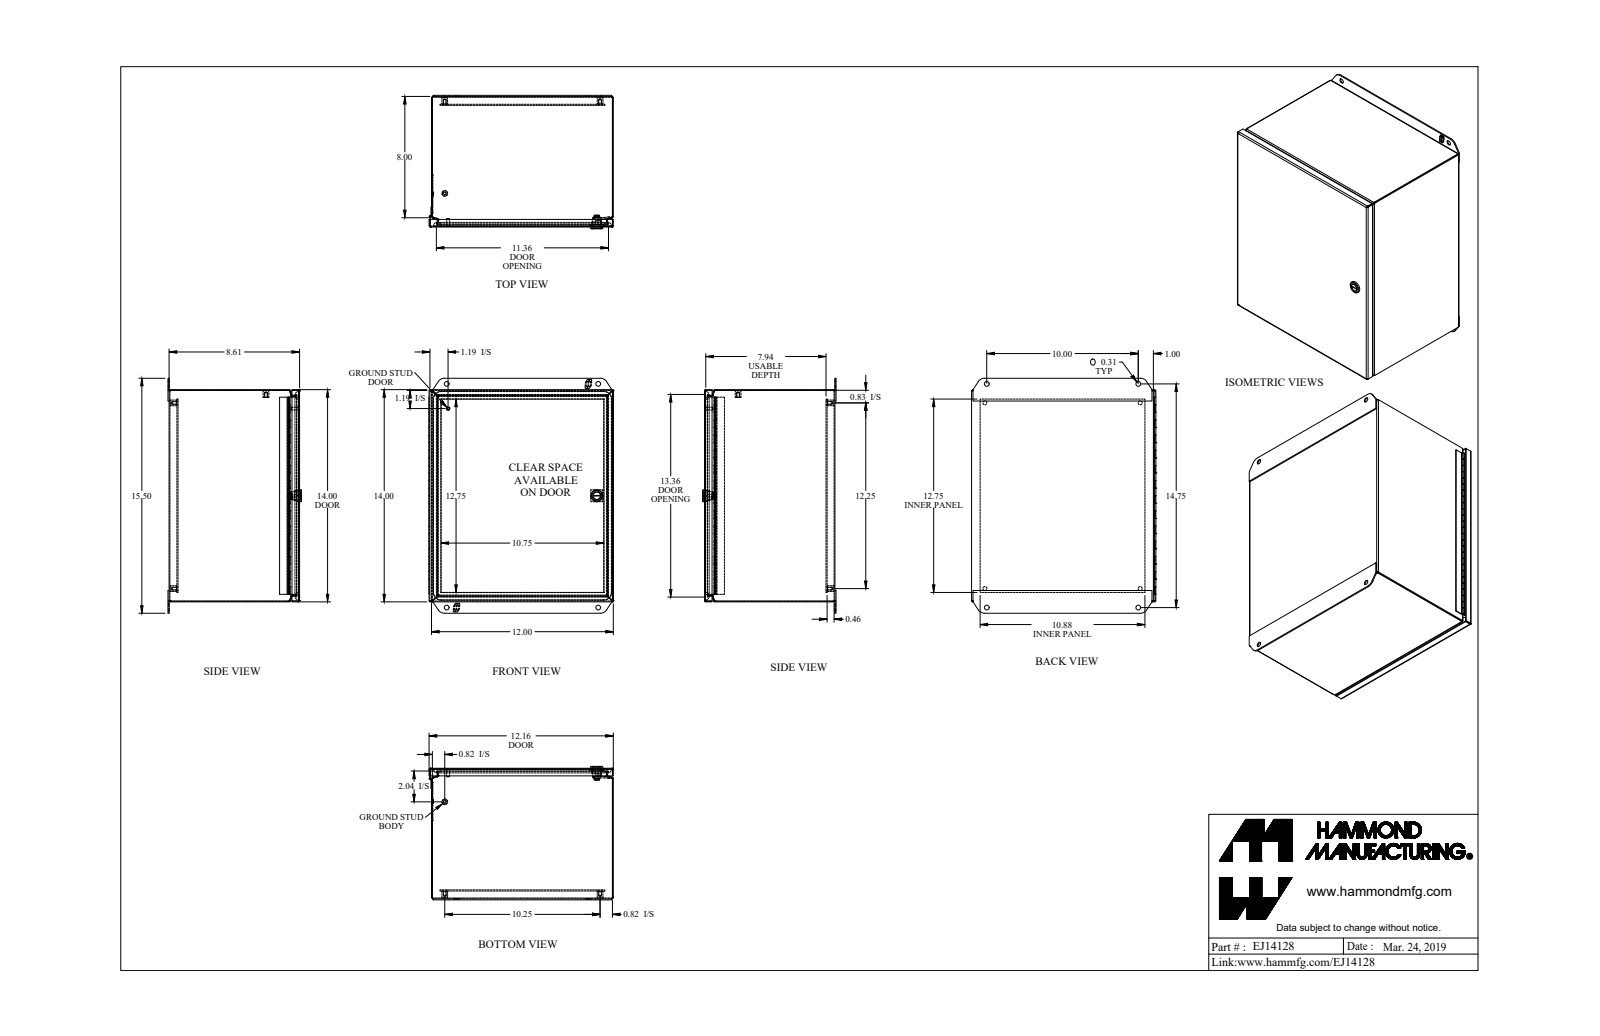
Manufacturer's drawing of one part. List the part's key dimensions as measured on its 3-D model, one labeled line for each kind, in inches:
Part name (STEP PRODUCT): EJ14128_Default
STEP written by: SolidWorks 2019 (CONFIG_CONTROL_DESIGN)
Units: inches
Bodies: 16 solids, 739 faces (409 planar, 238 cylindrical, 92 other)
Overall size (bounding box): 15.5 × 12.165 × 8.805
Volume: 64.11 in³ · Surface area: 2 131 in²
Round holes (diameter × count): ⌀0.156 ×5, ⌀0.265 ×4, ⌀0.313 ×4, ⌀0.05 ×1, ⌀0.516 ×1
Round bosses / shafts (diameter × count): ⌀0.375 ×5, ⌀0.788 ×1, ⌀0.535 ×1, ⌀0.496 ×1, ⌀0.435 ×1, ⌀0.25 ×1, ⌀0.188 ×1, ⌀0.1 ×1
Partial cylindrical surfaces — rounded edges, fillets, slot ends (radius × count): R0.029 ×16, R0.086 ×16, R0.281 ×10, R0.25 ×4, R0.499 ×4, R0.5 ×4, R0.06 ×2, R0.539 ×2
Main face-to-face distances: 0.057, 8.554, 11.943, 13.943, 0.072, 0.589, 8.611, 8.497, 0.46, 0.517
Hole centre spacings: 12.25, 6.129, 10.202, 15.972, 1.256, 1.257, 13.5, 13.5
